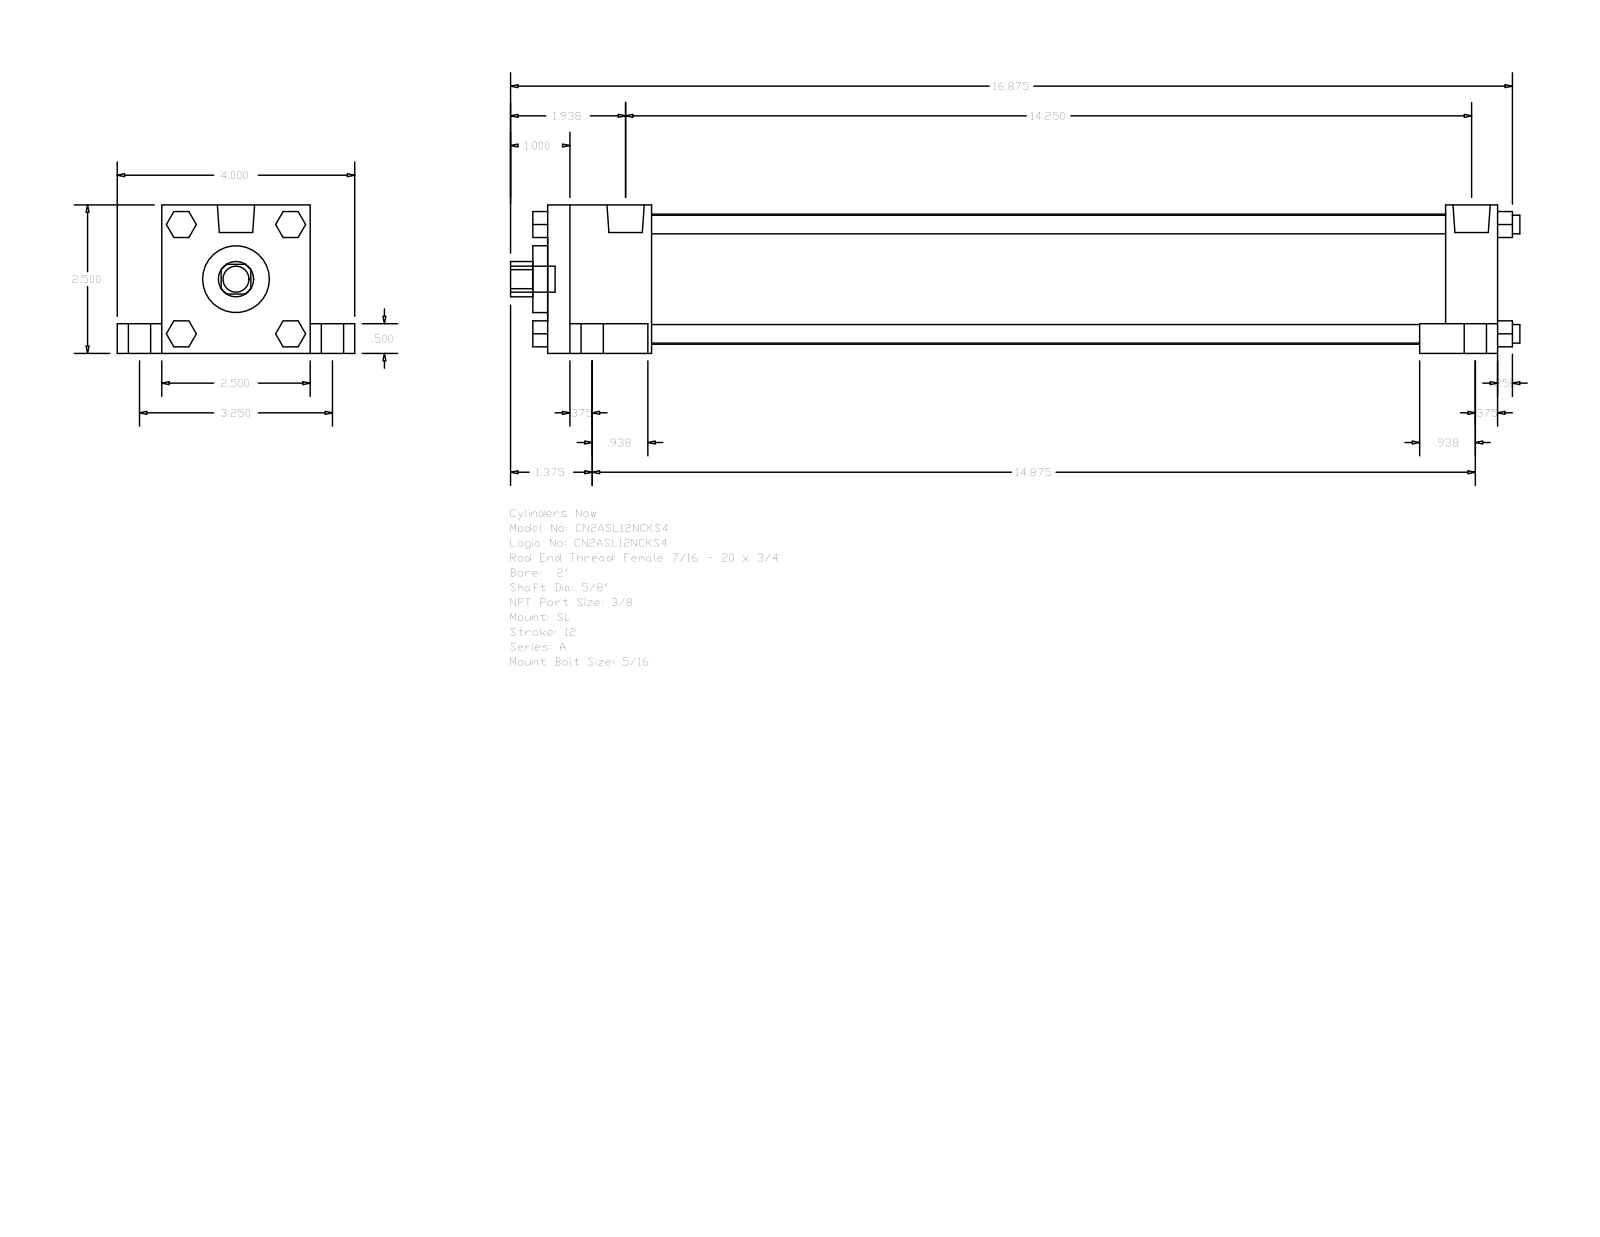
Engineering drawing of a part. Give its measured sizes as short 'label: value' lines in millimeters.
name: A_SL__0200_0.625
written by: GSSL Pune (CONFIG_CONTROL_DESIGN)
unit: mm
bodies: 0 solids, 148 faces (112 planar, 36 cylindrical, 0 other)
size: 431.8 × 101.6 × 63.5
holes: 1× ⌀15.88, 1× ⌀28.57, 1× ⌀55.63
bosses: 4× ⌀15.88, 4× ⌀9.53, 4× ⌀7.94, 4× ⌀5.56, 2× ⌀15.93, 1× ⌀11.11
rounds: 1× R7.54
face distances: 63.5, 406.39, 50.8, 12.7, 19.05, 82.55, 44.45, 361.94, 384.17, 339.72
